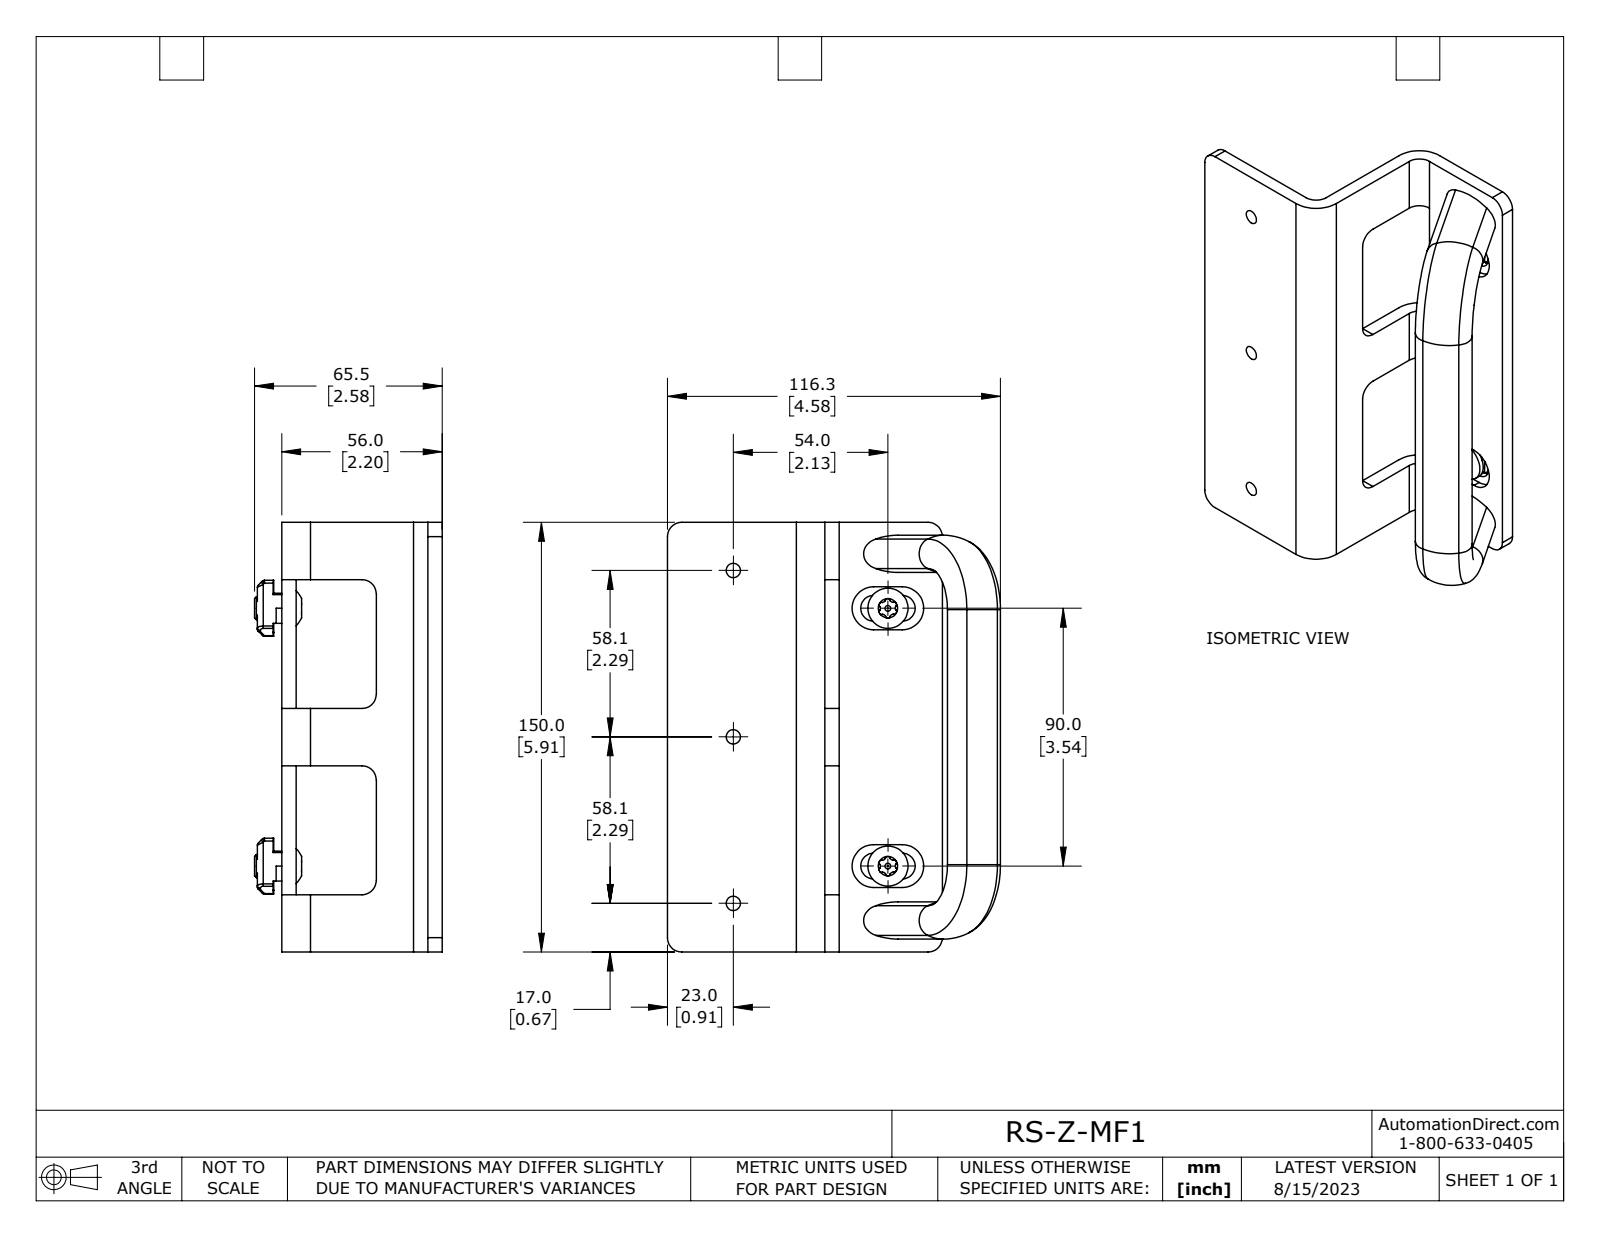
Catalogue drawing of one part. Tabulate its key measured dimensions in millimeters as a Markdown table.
| quantity | value |
| --- | --- |
| part name | RS-Z-MF1 |
| STEP written by | SolidWorks 2021 (AUTOMOTIVE_DESIGN) |
| units | millimeters |
| bodies | 8 solids, 361 faces (144 planar, 173 cylindrical, 44 other) |
| overall size | 150 × 116.3 × 65.5 |
| volume | 134 800 mm³ |
| surface area | 57 080 mm² |
| round holes (diameter × count) | 5 × 3, 4.9 × 2, 6.8 × 2, 6.8 × 2 |
| round bosses / shafts (diameter × count) | 8 × 4, 15.2 × 2, 14 × 2, 2 × 2 |
| partial cylindrical surfaces (radius × count) | 0.3 × 48, 1 × 30, 1.4 × 24, 5 × 10, 5.5 × 6, 16.2 × 6, 0.5 × 4, 2 × 4 |
| main face-to-face distances | 5, 51, 46, 56, 2.5, 50, 55, 96, 41, 150 |
| hole center spacings | 19.7, 58.1, 109.1, 55.5, 55.6, 59.3, 59.3, 70.2 |
